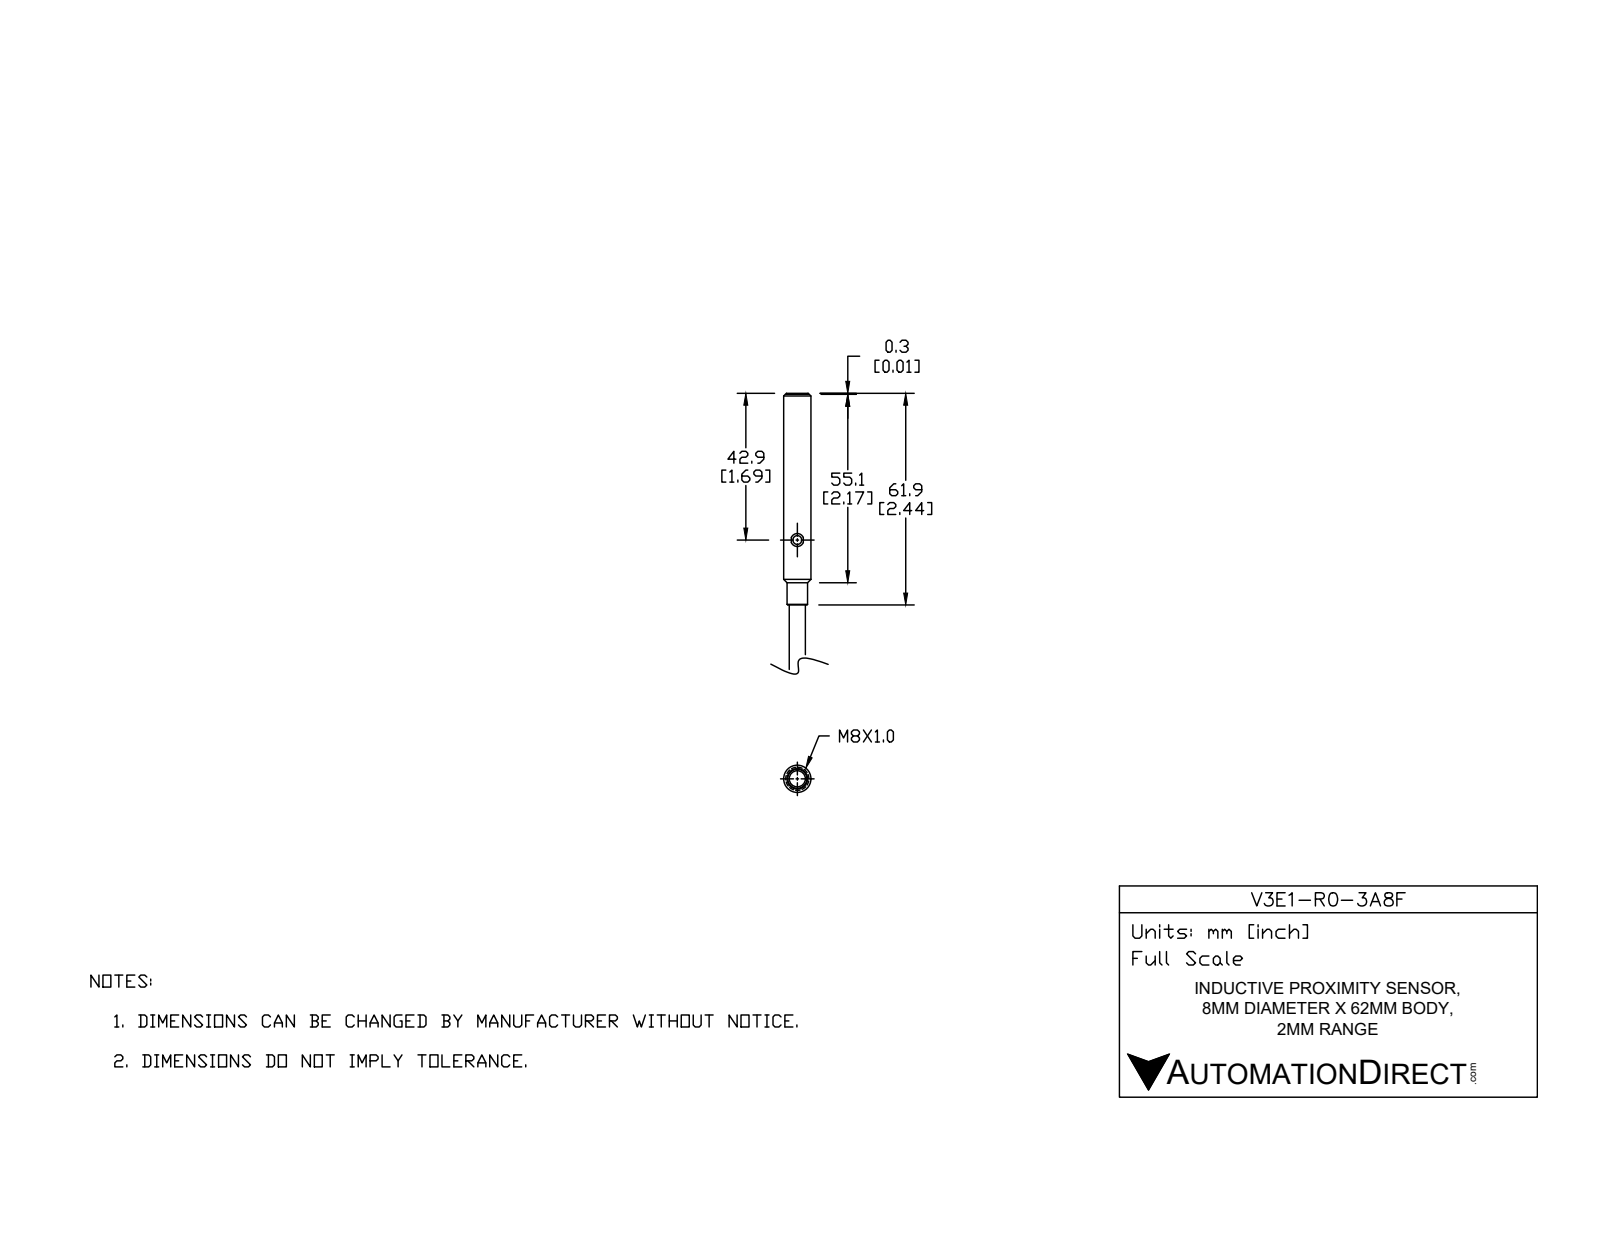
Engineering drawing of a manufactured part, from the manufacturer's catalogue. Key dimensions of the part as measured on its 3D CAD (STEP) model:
Part name (STEP PRODUCT): V3E1_3A_fig
STEP written by: ST-DEVELOPER v16.7 (AUTOMOTIVE_DESIGN)
Units: millimetres
Bodies: 1 solid, 17 faces (6 planar, 7 cylindrical, 4 other)
Overall size (bounding box): 101.9 × 8 × 8
Volume: 3 633 mm³ · Surface area: 2 189 mm²
Round holes (diameter × count): ⌀2.6 ×1
Round bosses / shafts (diameter × count): ⌀8 ×1, ⌀6.5 ×1, ⌀6 ×1, ⌀4.7 ×1
Partial cylindrical surfaces — rounded edges, fillets, slot ends (radius × count): R1.9 ×1
Main face-to-face distances: 101.9, 61.9, 40, 1.1, 61.6, 101.6
